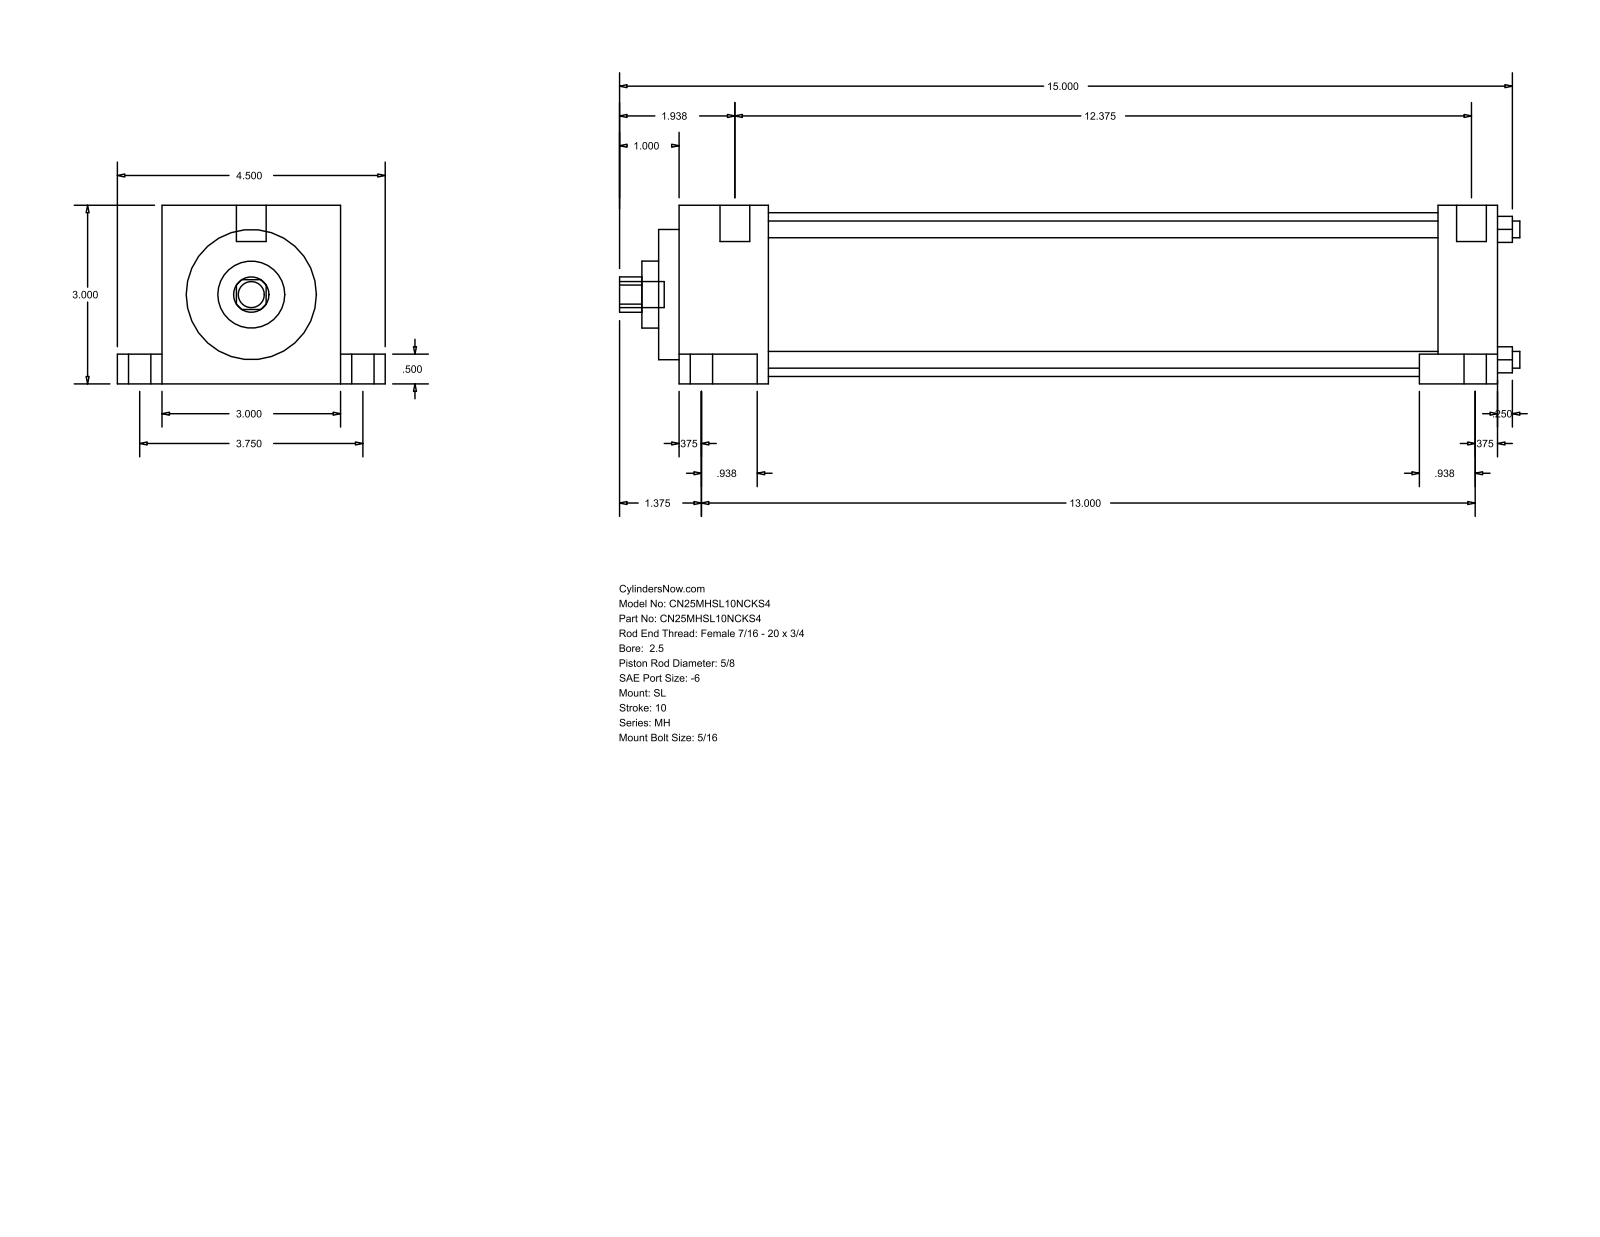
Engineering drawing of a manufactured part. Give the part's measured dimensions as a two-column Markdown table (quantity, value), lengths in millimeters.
| quantity | value |
| --- | --- |
| part name | MH_SL__0250_0.625 |
| STEP written by | GSSL Pune (CONFIG_CONTROL_DESIGN) |
| units | millimeters |
| bodies | 0 solids, 86 faces (61 planar, 25 cylindrical, 0 other) |
| overall size | 384.18 × 114.3 × 76.2 |
| round holes (diameter × count) | 7.14 × 4, 15.88 × 1, 28.57 × 1, 55.55 × 1, 69.85 × 1 |
| round bosses / shafts (diameter × count) | 15.88 × 2, 9.53 × 2, 5.56 × 2, 12.7 × 1, 11.11 × 1 |
| partial cylindrical surfaces (radius × count) | 7.54 × 1 |
| main face-to-face distances | 76.2, 25.4, 332.58, 357.98, 12.7, 63.5, 19.05, 95.25, 31.75, 324.64 |
| hole center spacings | 39.33, 55.62, 78.66 |
